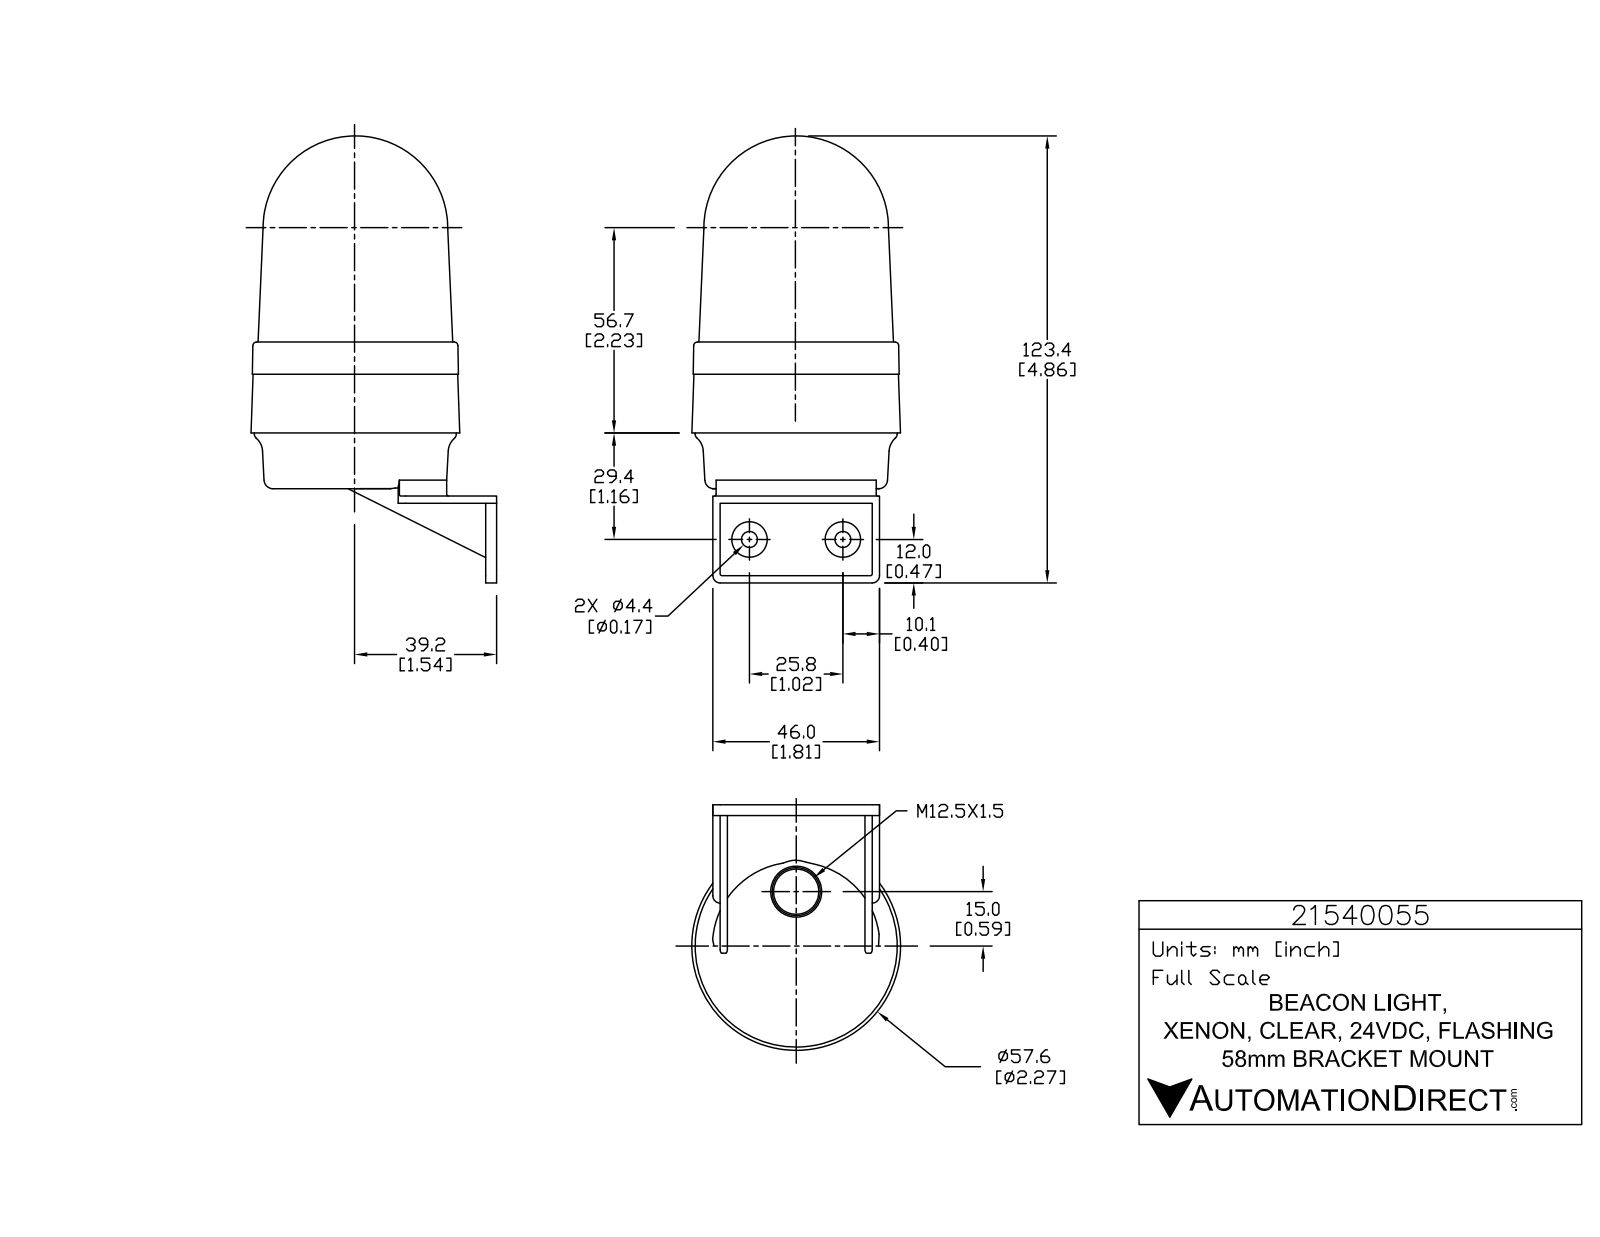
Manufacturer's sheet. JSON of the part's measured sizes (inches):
{"part_name": "21540055", "step_written_by": "SolidWorks 2015 (AUTOMOTIVE_DESIGN)", "units": "inches", "bodies": {"solids": 1, "faces": 828, "planar": 551, "cylindrical": 179, "other": 98}, "overall_size": [4.858, 2.852, 2.407], "volume_in3": 12.43, "surface_area_in2": 37.49, "round_holes": [[0.039, 3], [0.173, 2]], "round_bosses_or_shafts": [[0.226, 3], [0.056, 3], [0.386, 2], [2.197, 1]], "partial_cylinders_radius": [[0.008, 6], [0.008, 6], [0.008, 6], [0.02, 6], [0.131, 6], [0.079, 4], [0.004, 3], [0.005, 3]], "face_to_face_distances": [0.079, 0.157, 1.575, 1.654, 0.039, 0.118, 1.496, 0.866, 0.945, 0.764], "hole_center_spacings": [1.016]}
